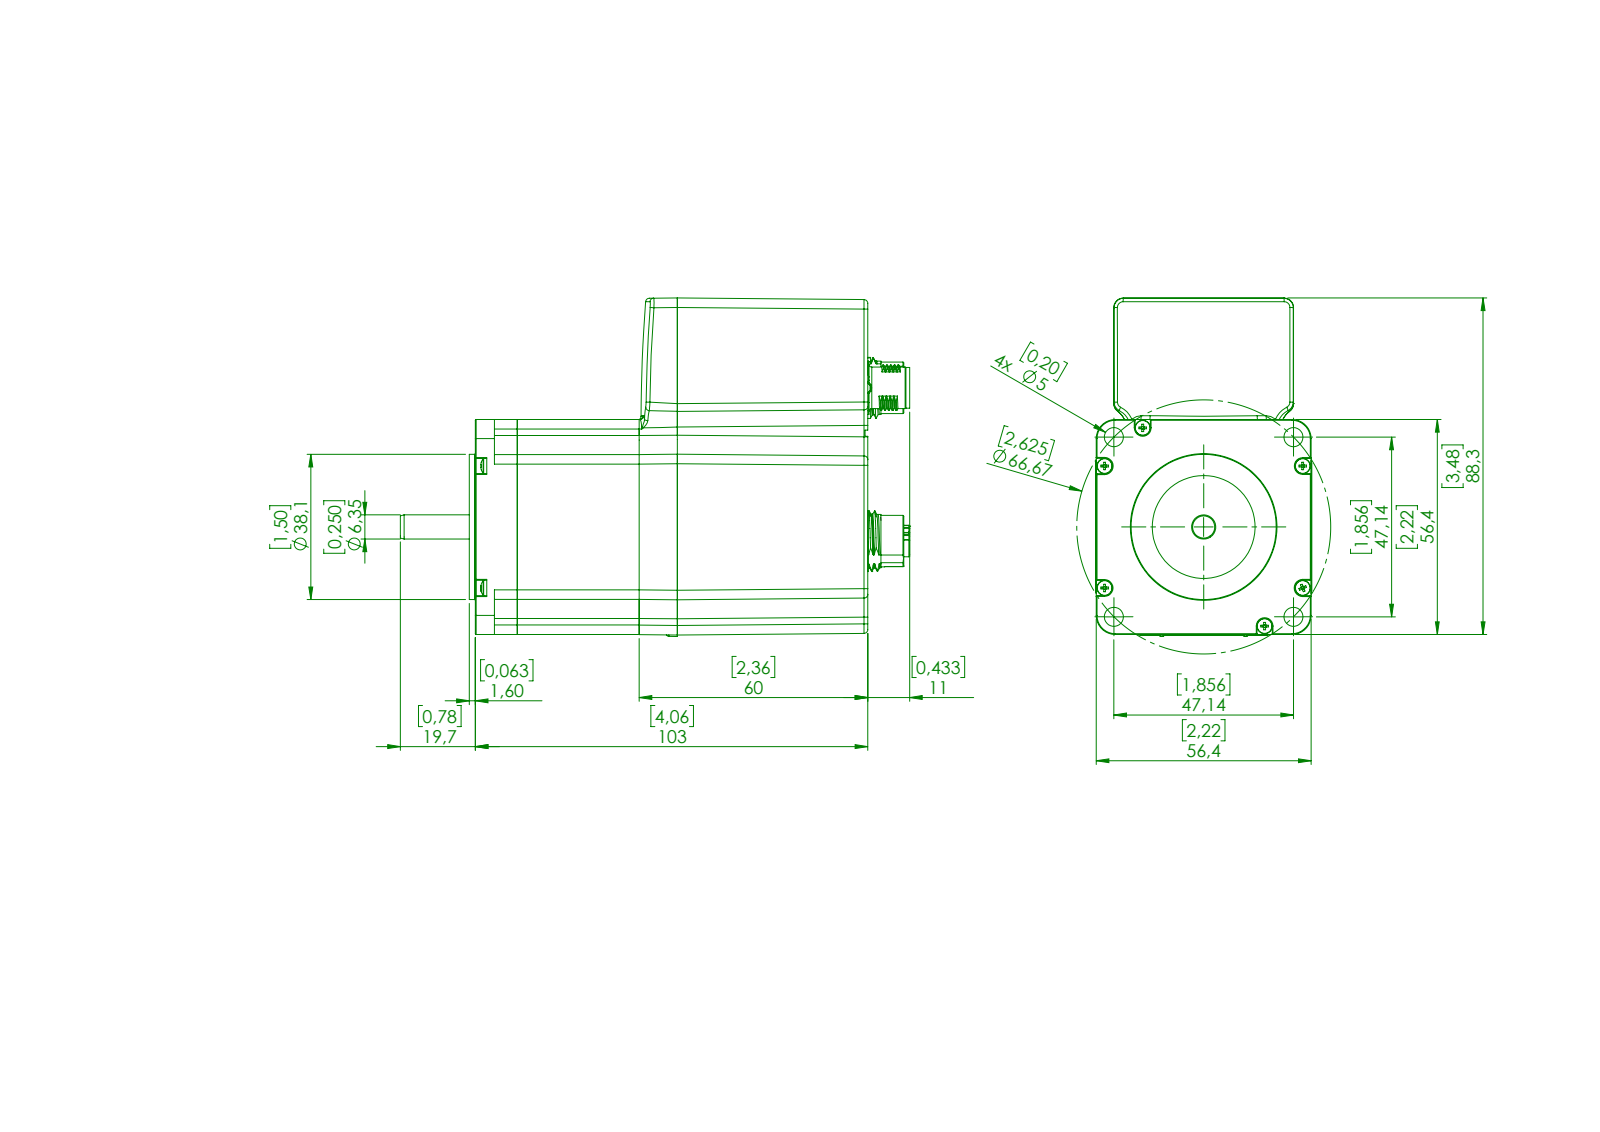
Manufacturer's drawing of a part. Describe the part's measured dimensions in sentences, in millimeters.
The part is named "O-ring_F_ILong; Housing MIS23 G2 Housing R10 SOLID; MM4100 V1_0 Rear Cover MIS23 G2 SOLID; Nema23 montado_F_ILong (+8 more)". Its 3-D file was written by "SolidWorks 2016 (CONFIG_CONTROL_DESIGN)". It is 16 solids with 2517 faces: 874 planar, 734 cylindrical and 909 other. Overall it measures 133.7 by 88.83 by 56.67 millimeters. Its volume is 390 979 cubic millimeters and its surface area 67 925 square millimeters. Round holes: 27 of diameter 1, 6 of diameter 2, 6 of diameter 2.5, 4 of diameter 5, 3 of diameter 12.2, 2 of diameter 1.52, 2 of diameter 8.6, 2 of diameter 11.13, 2 of diameter 14.6, 1 of diameter 3.3, 1 of diameter 4, 1 of diameter 8.3. Round bosses or shafts: 17 of diameter 1.1, 17 of diameter 0.6, 13 of diameter 1.6, 7 of diameter 1, 5 of diameter 4, 4 of diameter 13.25, 3 of diameter 13.5, 3 of diameter 0.22. Partial cylindrical surfaces (rounded edges, fillets, slot ends): 64 of radius 0.2, 32 of radius 0.1, 29 of radius 2.5, 18 of radius 5, 16 of radius 1, 12 of radius 0.8, 10 of radius 0.15, 8 of radius 0.25. The main face-to-face distances are 10, 32, 42, 49.3, 59.3, 91.3, 56.4, 4.75, 11, 102.3. The hole center spacings are 2.5, 3.54, 39.64, 0.62, 7.78, 7.95, 30, 30.53.
